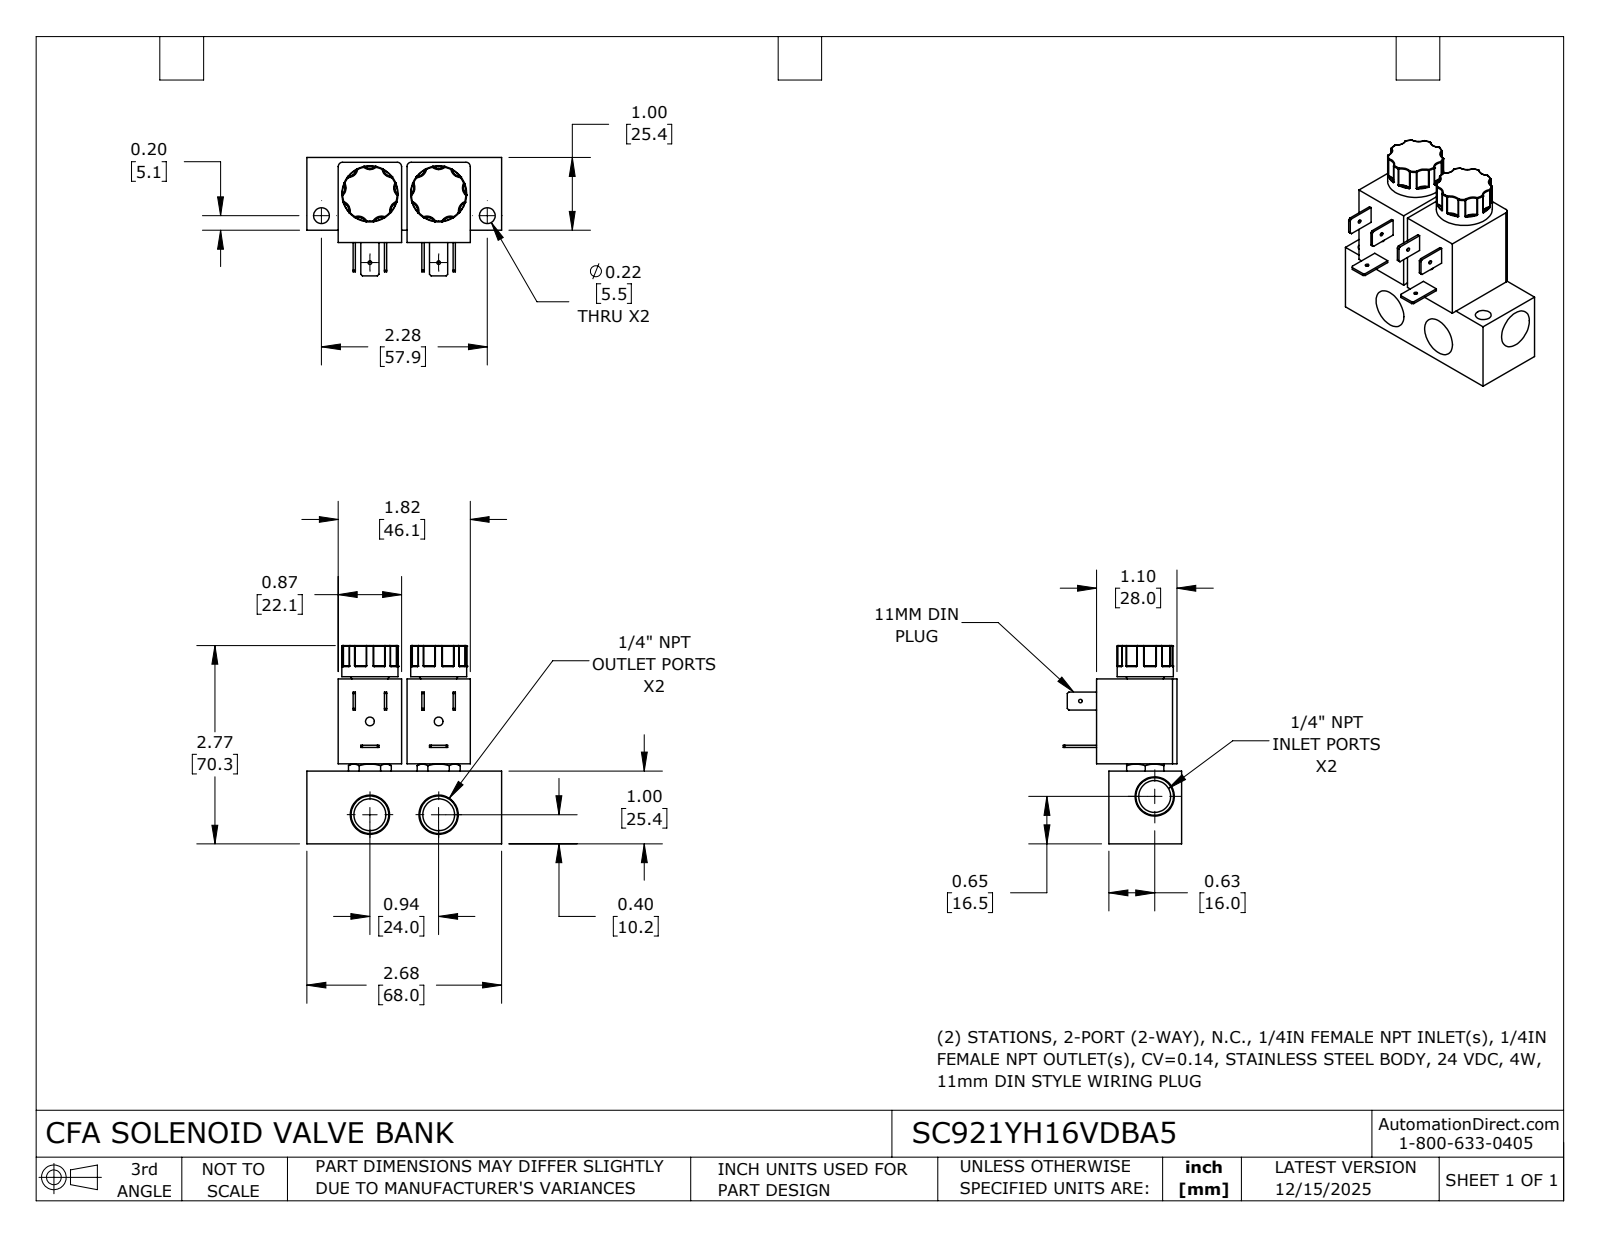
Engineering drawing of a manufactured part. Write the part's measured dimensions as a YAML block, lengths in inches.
part_name: "SC921YH16VDBA5"
step_written_by: "SolidWorks 2024 (CONFIG_CONTROL_DESIGN)"
units: inches
bodies: {solids: 1, faces: 446, planar: 100, cylindrical: 96, other: 250}
overall_size: [2.725, 2.677, 1.627]
volume: 4.833
surface_area: 34.57
round_holes:
  - {diameter: 0.05, count: 3}
  - {diameter: 0.438, count: 3}
  - {diameter: 0.12, count: 2}
  - {diameter: 0.217, count: 2}
round_bosses_or_shafts:
  - {diameter: 0.77, count: 2}
partial_cylinders:
  - {radius: 0.01, count: 36}
  - {radius: 0.133, count: 18}
  - {radius: 0.06, count: 4}
face_to_face_distances: [1, 0.945, 0.87, 1.169, 0.169, 0.065, 0.935, 1.104, 0.431, 1.301]
hole_center_spacings: [0.945, 1.282, 1.593, 0.928, 0.93, 1.662, 1.735, 1.738]
